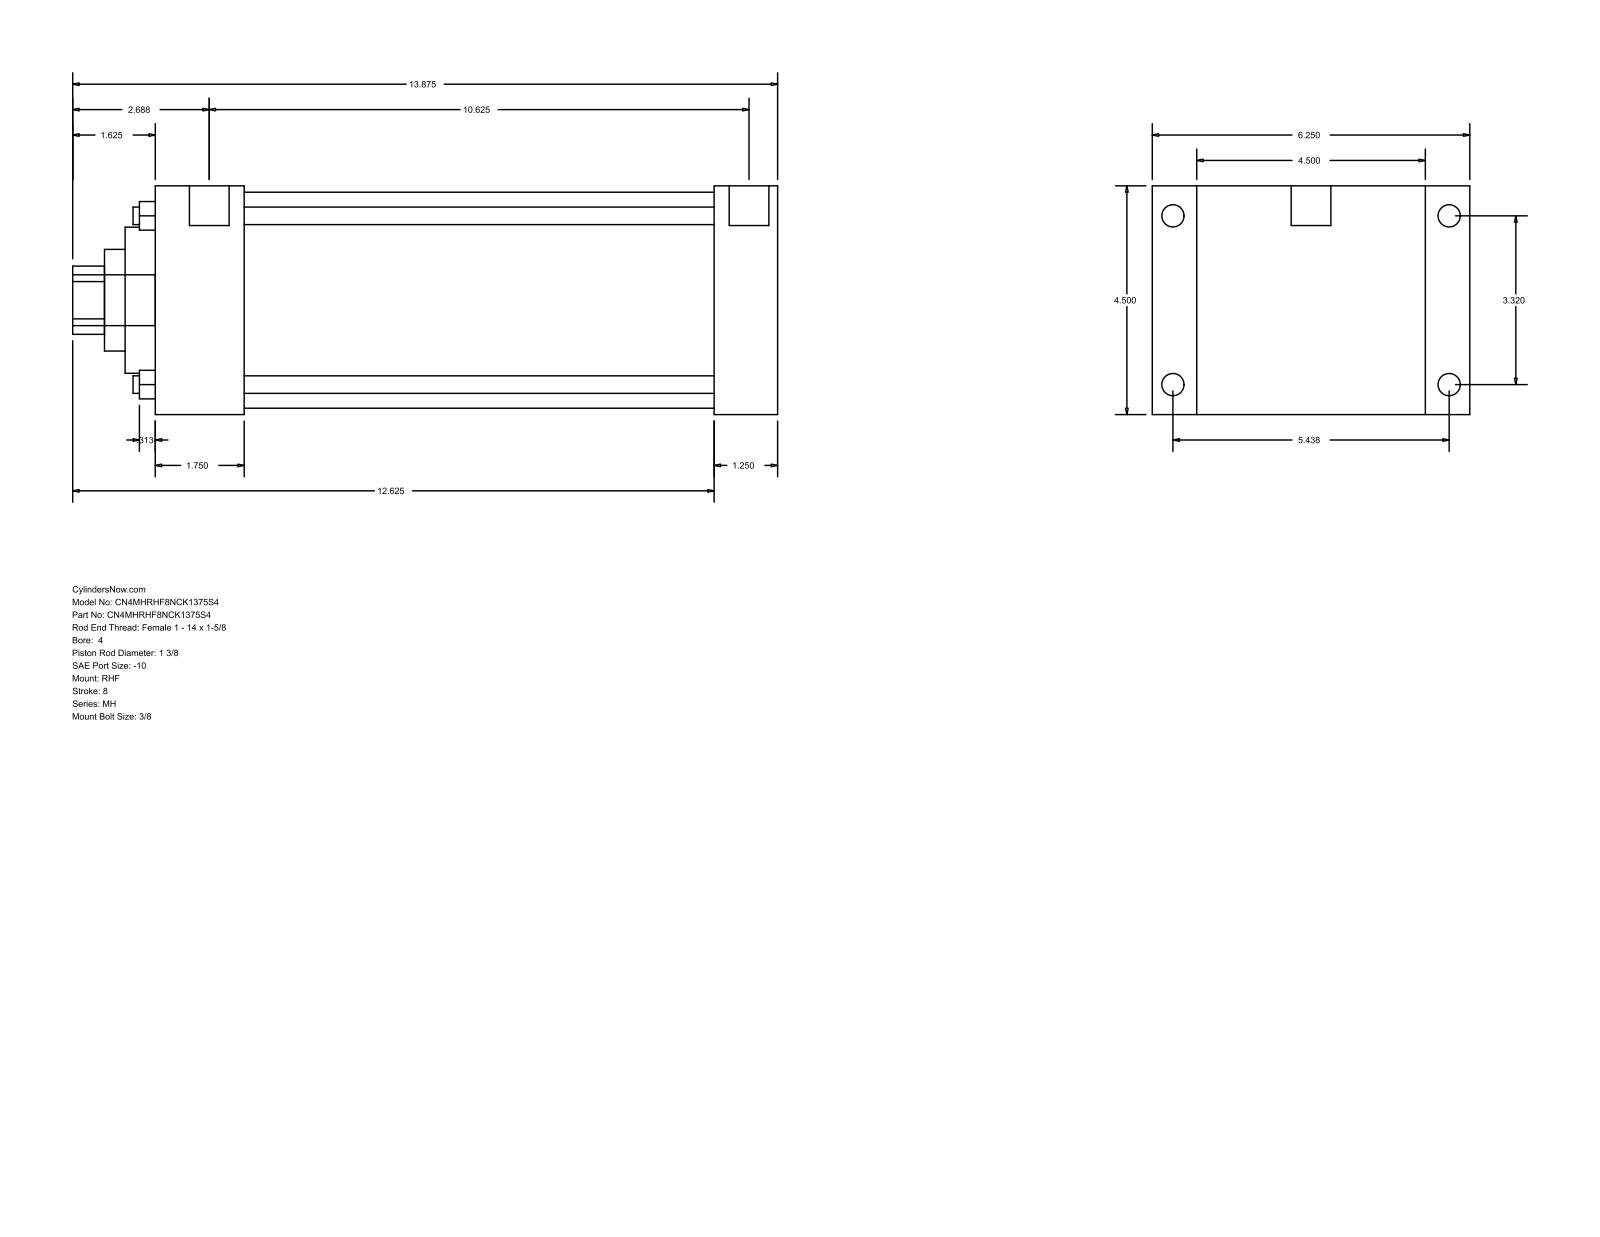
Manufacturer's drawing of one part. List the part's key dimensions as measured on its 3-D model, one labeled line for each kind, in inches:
Part name (STEP PRODUCT): MH_RHF__0400_1.375
STEP written by: GSSL Pune (CONFIG_CONTROL_DESIGN)
Units: inches
Bodies: 0 solids, 90 faces (61 planar, 29 cylindrical, 0 other)
Overall size (bounding box): 13.875 × 6.25 × 4.5
Round holes (diameter × count): ⌀0.345 ×4, ⌀1.375 ×1, ⌀2 ×1, ⌀2.875 ×1, ⌀4.25 ×1
Round bosses / shafts (diameter × count): ⌀0.438 ×4, ⌀0.344 ×4, ⌀0.781 ×2, ⌀1 ×1
Partial cylindrical surfaces — rounded edges, fillets, slot ends (radius × count): R0.672 ×1
Main face-to-face distances: 4.5, 12.25, 11, 1.25, 0.875, 5.375, 1.75, 9.25, 10.5, 6.25
Hole centre spacings: 2.347, 3.32, 4.695
